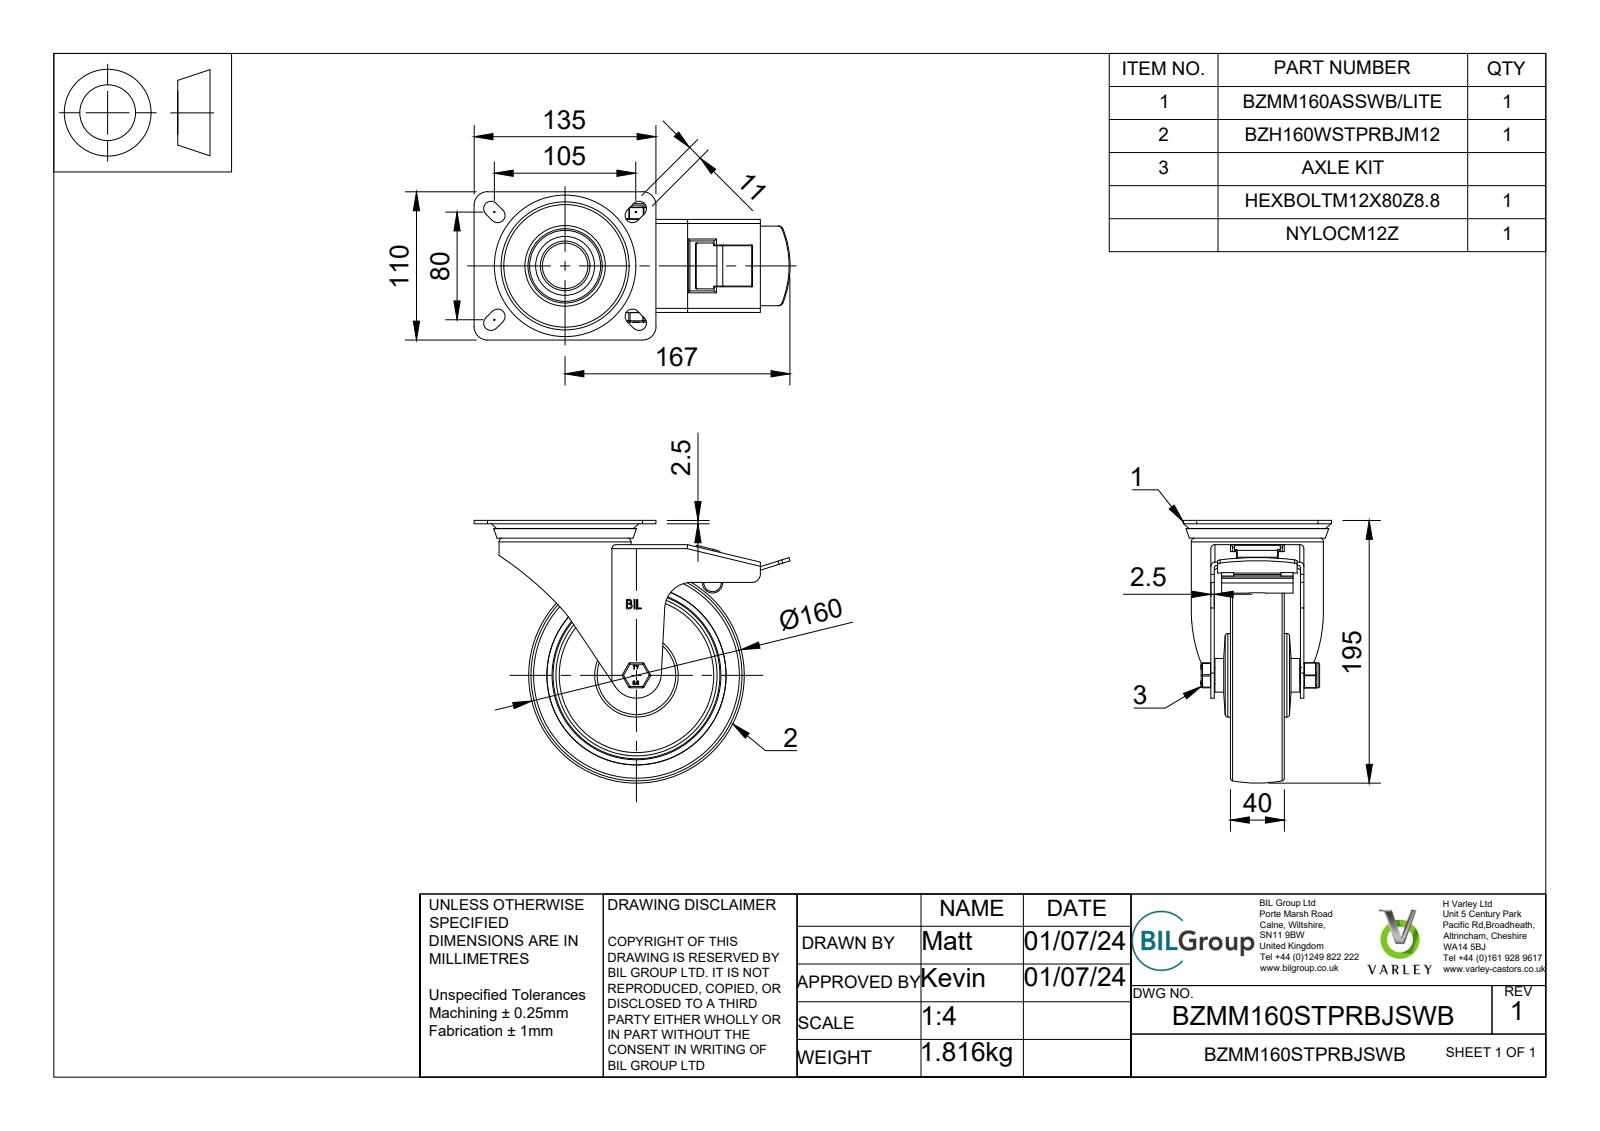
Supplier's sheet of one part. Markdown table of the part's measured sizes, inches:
| quantity | value |
| --- | --- |
| part name | BZMM160STPRBJSWB v3; BZH160WSTPRBJM12 v1; 65 SHORE A THERMOPLASTIC RUBBER TYRE; POLYPROPYLENE RIM (+7 more) |
| STEP written by | Autodesk Translation Framework v13.14.0.145 (AUTOMOTIVE_DESIGN) |
| units | inches |
| bodies | 65 solids, 919 faces (377 planar, 213 cylindrical, 329 other) |
| overall size | 9.232 × 7.677 × 4.331 |
| volume | 39.98 in³ |
| surface area | 465.9 in² |
| round holes (diameter × count) | 0.402 × 1, 0.472 × 1, 0.496 × 1, 0.551 × 1, 0.787 × 1, 1.122 × 1, 1.213 × 1, 1.329 × 1, 1.565 × 1, 1.587 × 1, 1.594 × 1, 1.654 × 1 |
| round bosses / shafts (diameter × count) | 3.858 × 1, 3.071 × 1, 2.441 × 1, 2.224 × 1, 1.969 × 1, 1.89 × 1, 1.606 × 1, 1.232 × 1 |
| partial cylindrical surfaces (radius × count) | 0.02 × 19, 0.039 × 13, 0.059 × 12, 0.217 × 8, 0.118 × 7, 0.03 × 6, 0.079 × 4, 0.394 × 4 |
| main face-to-face distances | 0.098, 0.472, 1.486, 0.659, 0.915, 0.256, 0.571, 1.23, 2.146, 0.354 |
